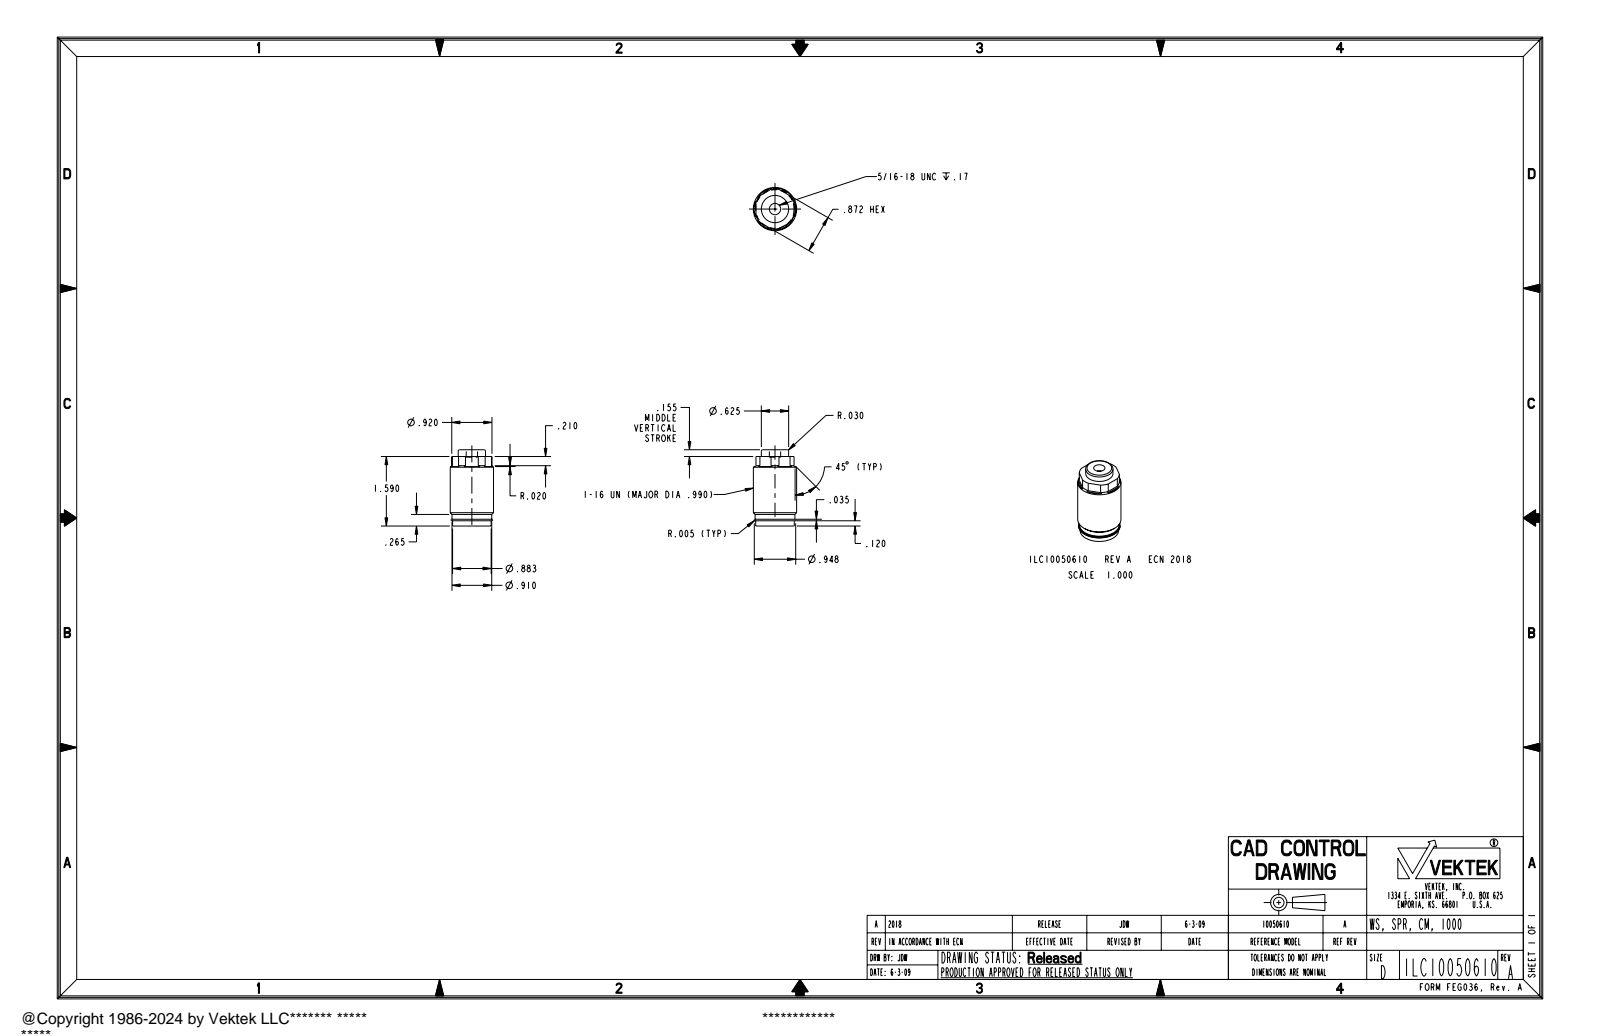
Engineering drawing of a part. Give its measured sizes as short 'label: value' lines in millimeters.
name: ILC10050610
written by: PRO/ENGINEER BY PARAMETRIC TECHNOLOGY CORPORATION, 2007460 (AUTOMOTIVE_DESIGN_CC2)
unit: mm
bodies: 1 solid, 52 faces (18 planar, 24 cylindrical, 10 other)
size: 44.3 × 25.1 × 25.1
volume: 19 580 mm³; area: 4 344 mm²
holes: 1× ⌀6.6
bosses: 1× ⌀25.1, 1× ⌀24.1, 1× ⌀23.1, 1× ⌀22.4, 1× ⌀15.9
rounds: 6× R0.5, 1× R11.7
face distances: 40.4, 44.3, 3.9, 22.1, 3, 37.3, 41.3, 40, 37, 0.4
